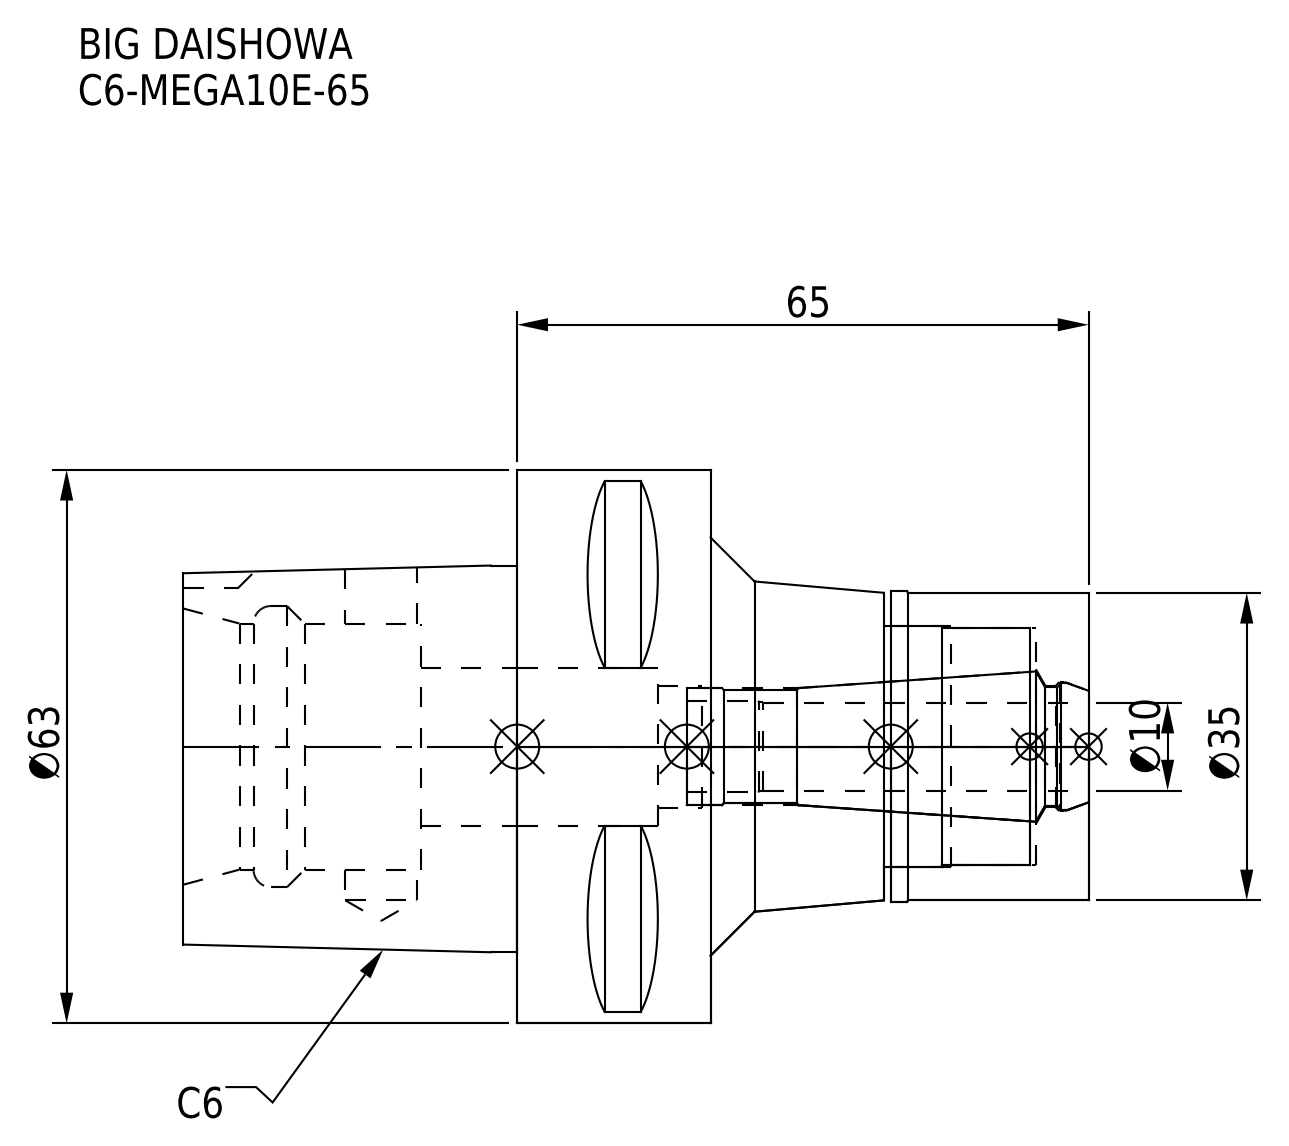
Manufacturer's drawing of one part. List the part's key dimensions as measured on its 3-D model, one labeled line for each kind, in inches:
Part name (STEP PRODUCT): DXF_TEMP_ASSY_ASM_4_ASM.stp; C6-MEGA10E-65-100_ASM.stp; C6-MEGA10E-65-100.stp; C6-MEGA10E-65_1.stp (+3 more)
STEP written by: SolidWorks 2019 (CONFIG_CONTROL_DESIGN)
Units: inches
Bodies: 2 solids, 94 faces (35 planar, 35 cylindrical, 24 other)
Overall size (bounding box): 4.055 × 2.48 × 2.48
Volume: 8.092 in³ · Surface area: 47.65 in²
Round holes (diameter × count): ⌀0.319 ×1, ⌀0.524 ×1, ⌀0.543 ×1, ⌀0.547 ×1, ⌀0.579 ×1, ⌀0.709 ×1, ⌀1.063 ×1, ⌀1.083 ×1, ⌀1.102 ×1, ⌀1.26 ×1
Round bosses / shafts (diameter × count): ⌀2.48 ×1, ⌀1.39 ×1, ⌀1.378 ×1
Partial cylindrical surfaces — rounded edges, fillets, slot ends (radius × count): R0.197 ×1
Main face-to-face distances: 0.866, 1.693, 2.559, 1.496, 4.055, 2.362, 1.063, 0.236, 0.886, 0.807
